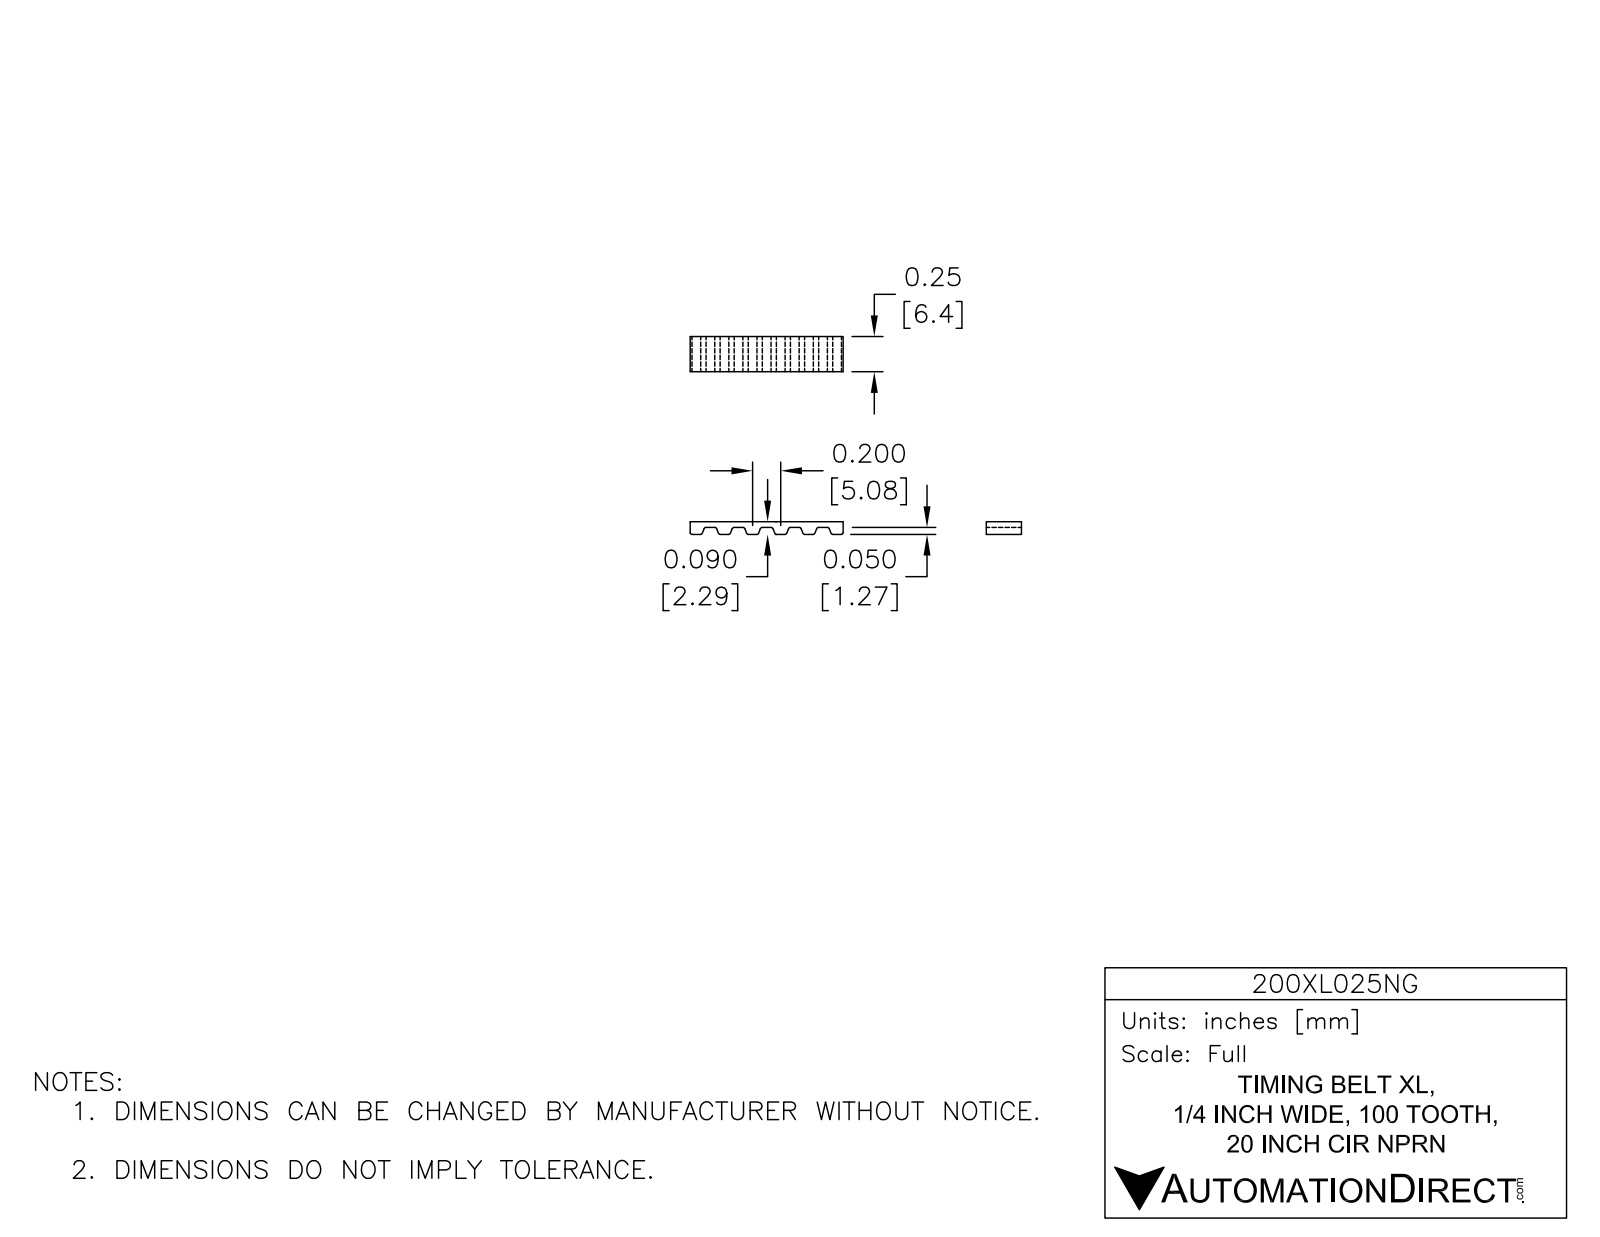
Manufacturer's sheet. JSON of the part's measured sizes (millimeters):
{"part_name": "200XL025NG", "step_written_by": "SolidWorks 2014 (AUTOMOTIVE_DESIGN)", "units": "millimeters", "bodies": {"solids": 1, "faces": 840, "planar": 360, "cylindrical": 480, "other": 0}, "overall_size": [210.5, 76.2, 6.4], "volume_mm3": 4460, "surface_area_mm2": 8703, "partial_cylinders_radius": [[0.4, 400], [37.1, 2], [38.1, 2]], "face_to_face_distances": [76.2, 1, 75.2, 6.4, 74.2, 9.1, 2.3, 73.9, 1.3, 72.9]}
